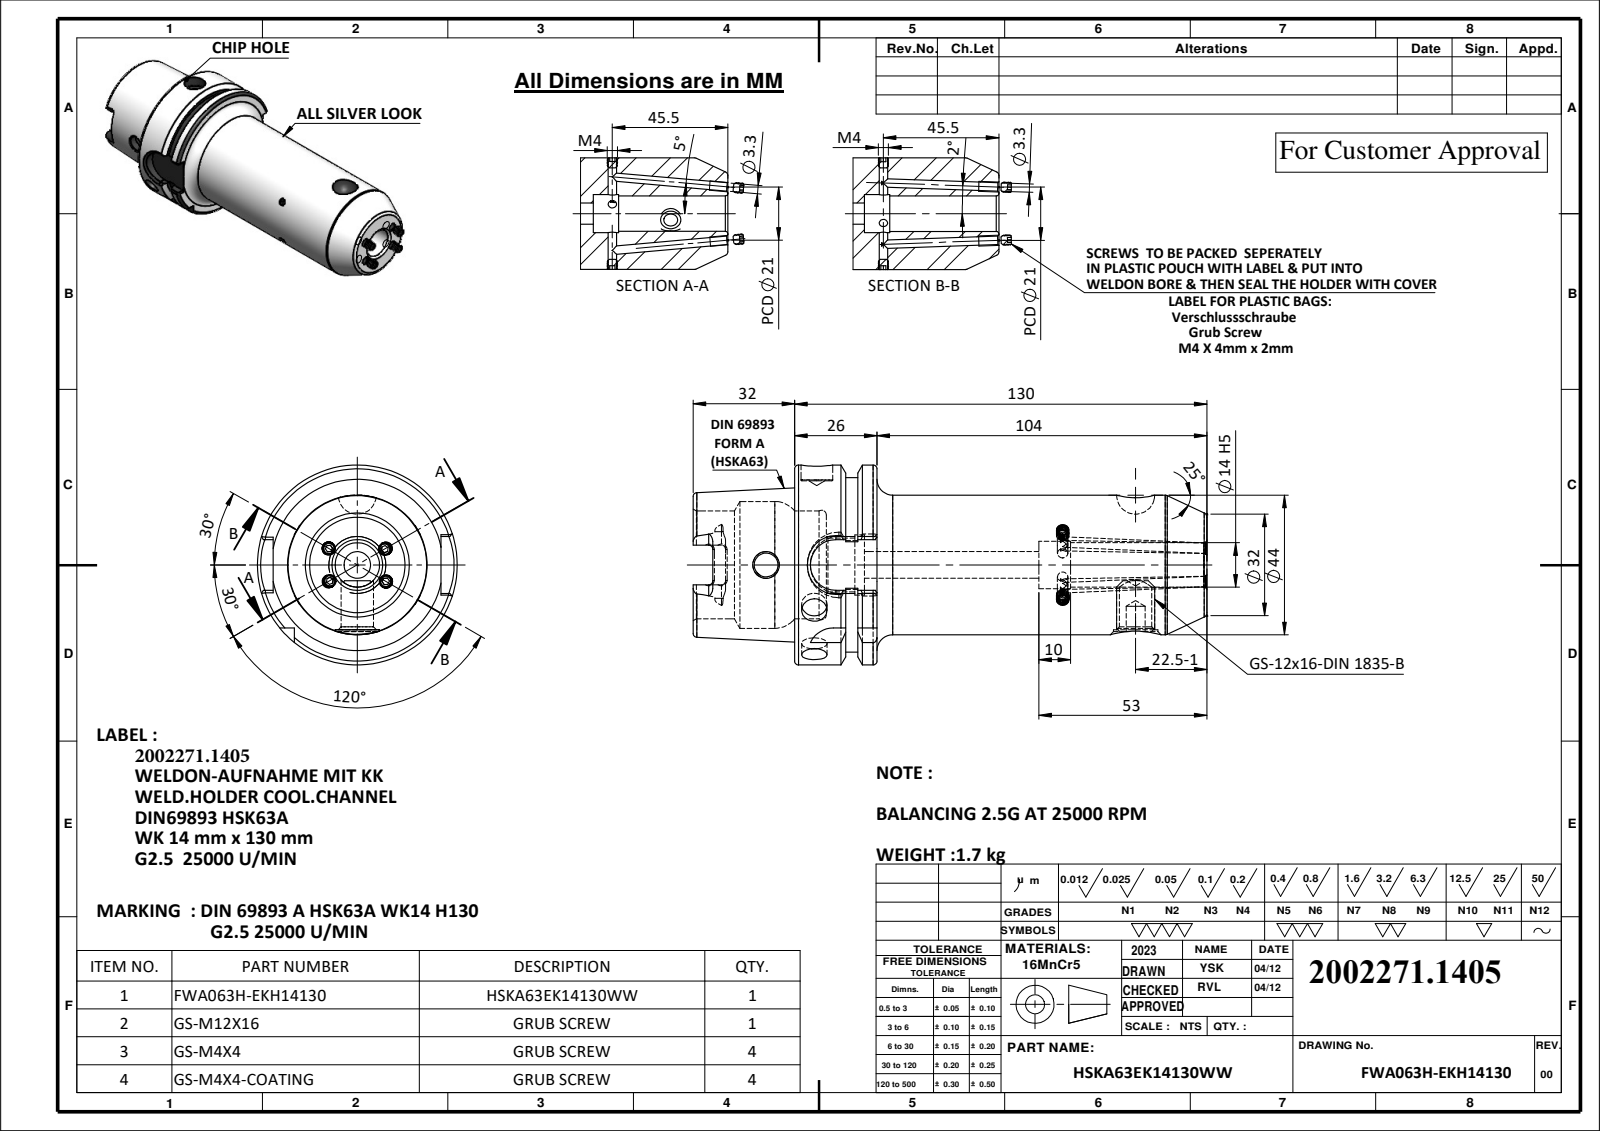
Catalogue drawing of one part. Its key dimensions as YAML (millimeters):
part_name: "HSKA63EK14130WW; GS-M4X4_DIN 913 - M4 x 4-N; GS-M12X16-DIN1835-B; GS-M4X4-COATING_DIN 913 - M4 x 4-N (+1 more)"
step_written_by: "SolidWorks 2023 (CONFIG_CONTROL_DESIGN)"
units: millimeters
bodies: {solids: 10, faces: 620, planar: 139, cylindrical: 165, other: 316}
overall_size: [168.34, 63, 63]
volume: 221629
surface_area: 43757
round_holes:
  - {diameter: 3.3, count: 8}
  - {diameter: 8, count: 2}
  - {diameter: 14, count: 2}
  - {diameter: 7.5, count: 1}
  - {diameter: 8.4, count: 1}
  - {diameter: 10, count: 1}
  - {diameter: 10.2, count: 1}
  - {diameter: 15, count: 1}
  - {diameter: 17, count: 1}
  - {diameter: 19, count: 1}
  - {diameter: 34, count: 1}
  - {diameter: 40, count: 1}
round_bosses_or_shafts:
  - {diameter: 4, count: 8}
  - {diameter: 63, count: 1}
  - {diameter: 55, count: 1}
  - {diameter: 44, count: 1}
  - {diameter: 12, count: 1}
partial_cylinders:
  - {radius: 1.3, count: 6}
  - {radius: 2.88, count: 4}
  - {radius: 8, count: 2}
  - {radius: 9, count: 1}
face_to_face_distances: [10, 25.95, 15.95, 130, 120, 104.05, 32, 42, 57.95, 162]
hole_center_spacings: [100.5]
